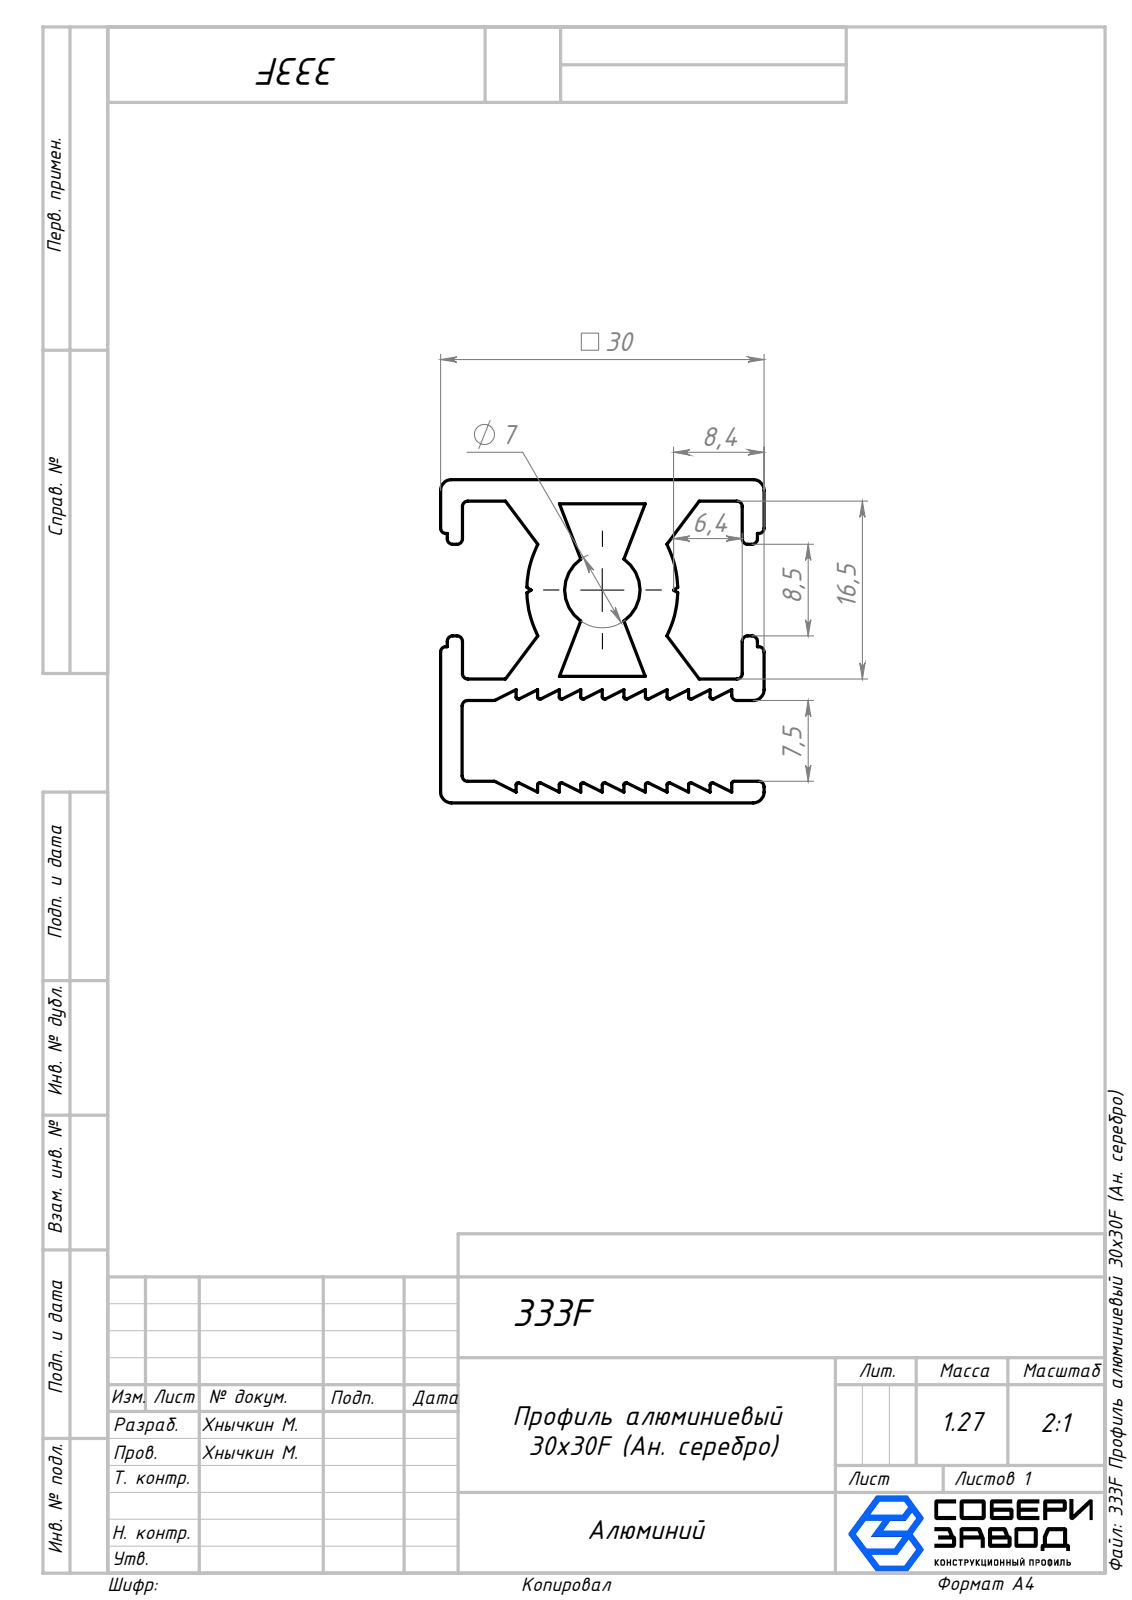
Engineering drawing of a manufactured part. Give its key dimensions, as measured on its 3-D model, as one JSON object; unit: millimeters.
{"part_name": "333F Профиль алюминиевый 30х30F (Ан. серебро)", "step_written_by": "SolidWorks 2026 (AUTOMOTIVE_DESIGN)", "units": "millimeters", "bodies": {"solids": 1, "faces": 147, "planar": 92, "cylindrical": 55, "other": 0}, "overall_size": [1400, 30, 30], "volume_mm3": 472194, "surface_area_mm2": 427442, "partial_cylinders_radius": [[0.2, 23], [0.5, 20], [1, 5], [9.37, 2], [3.5, 1]], "face_to_face_distances": [2, 30, 1.79, 2.68, 0.89, 4.47, 28, 0.9, 3.58, 16.25]}
